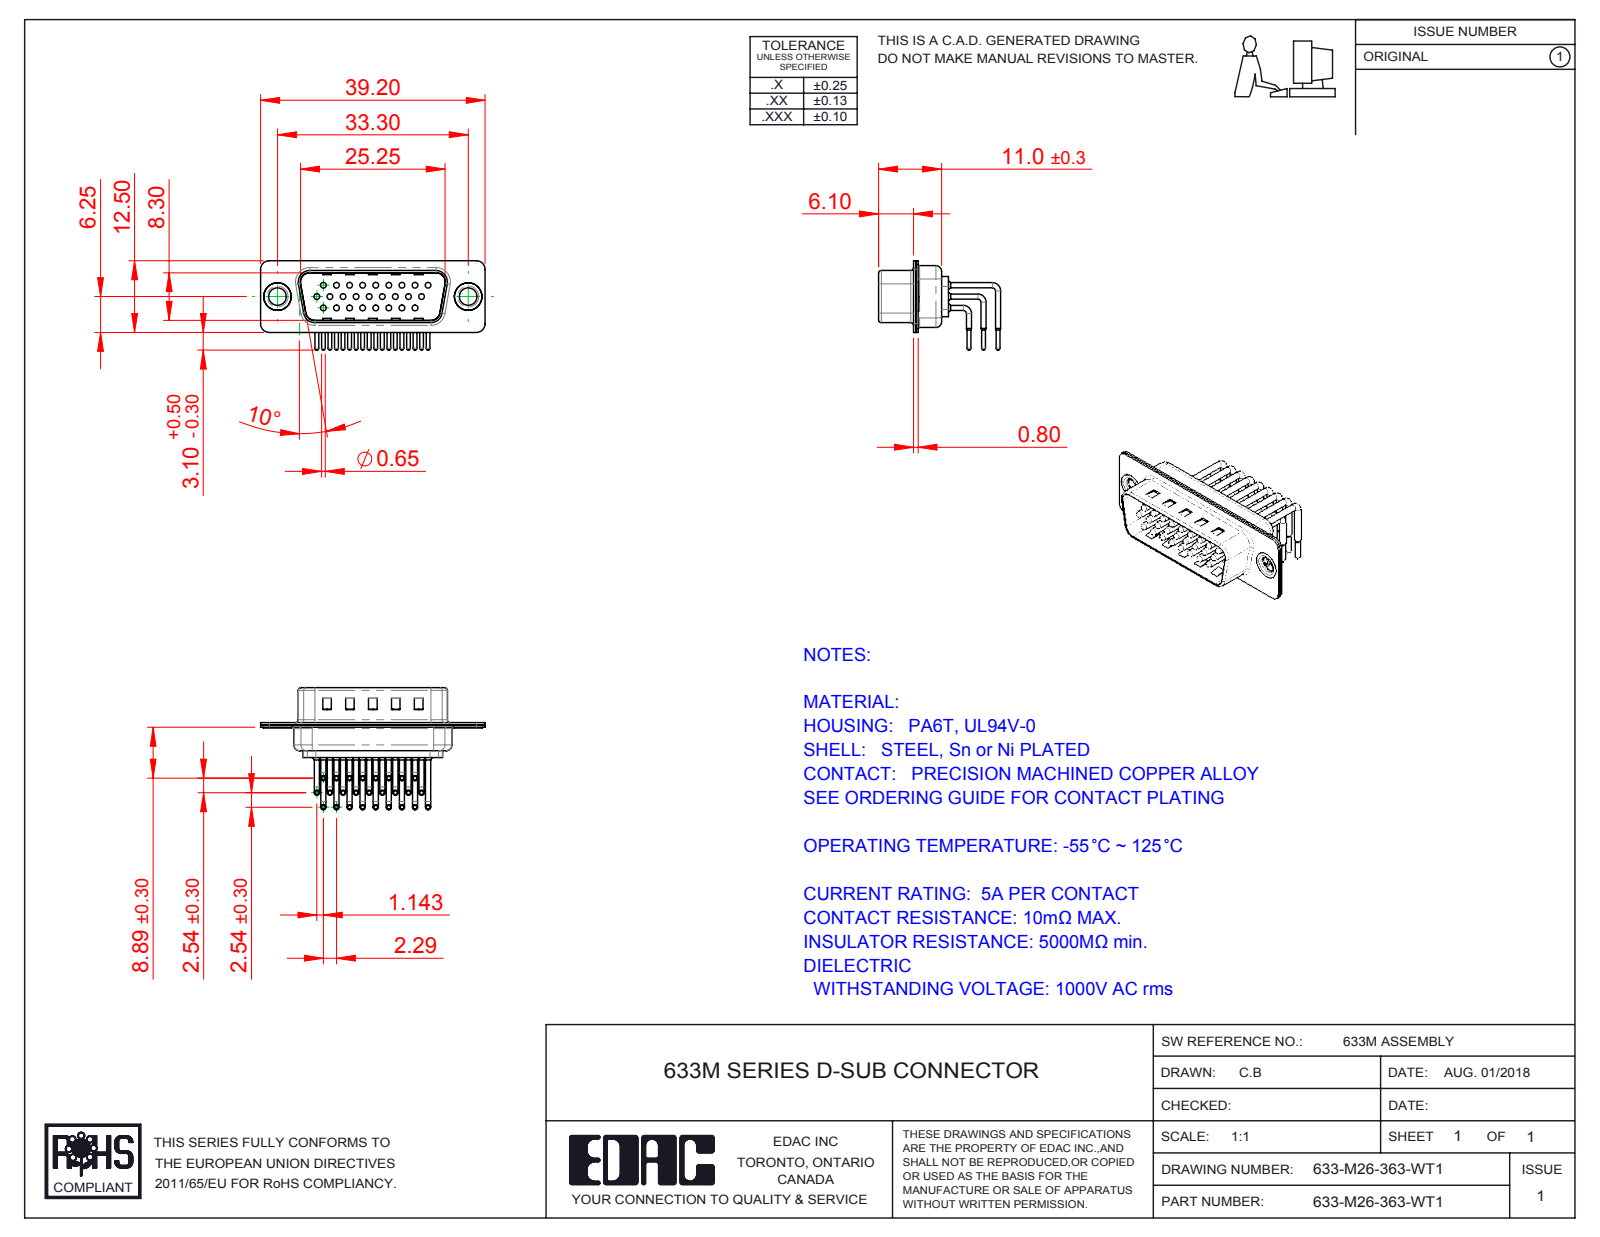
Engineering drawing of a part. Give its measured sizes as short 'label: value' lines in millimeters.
name: 633M Contact Row 3; 633M Contact Row 1; 633M Contact Row 2; 633M Shell Front_26 Contacts (+4 more)
written by: SolidWorks 2016 (CONFIG_CONTROL_DESIGN)
unit: mm
bodies: 31 solids, 3174 faces (1803 planar, 1053 cylindrical, 318 other)
size: 39.2 × 21.32 × 15.6
volume: 2 011 mm³; area: 6 546 mm²
holes: 26× ⌀1, 26× ⌀1.7, 26× ⌀2, 2× ⌀3.05, 2× ⌀4, 2× ⌀4.8
bosses: 52× ⌀0.9, 26× ⌀1.5, 26× ⌀0.65, 2× ⌀5, 2× ⌀4.9, 2× ⌀3.55
rounds: 26× R1.01, 16× R1.5, 12× R2, 8× R0.5, 8× R1.6, 4× R0.25, 4× R0.6, 4× R0.65
face distances: 0.4, 0.85, 9.55, 1.5, 8.7, 1.9, 1.25, 0.8, 10.4, 0.35
hole spacings: 3.96, 2.28, 4.57, 6.05, 2.29, 8.24, 6.86, 10.48
